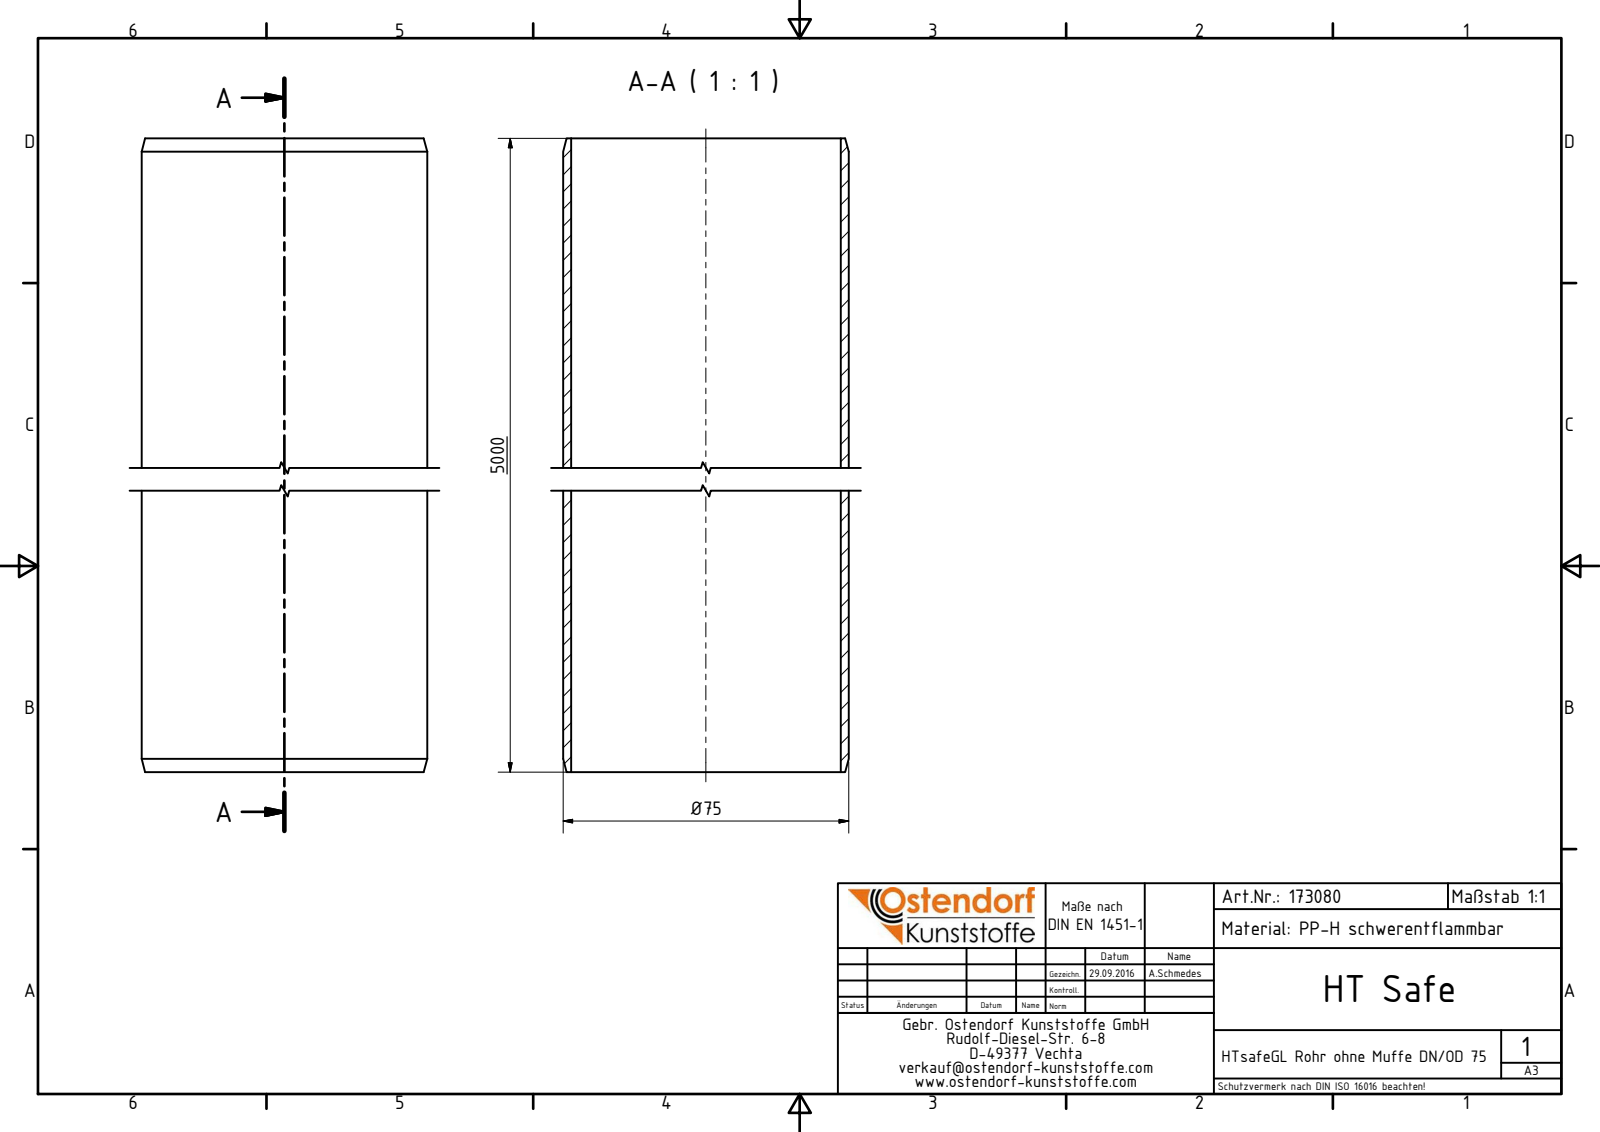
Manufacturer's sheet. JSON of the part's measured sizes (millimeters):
{"part_name": "173080 HTsafeGL DN_OD 75x5000", "step_written_by": "Autodesk Inventor 2016 (AUTOMOTIVE_DESIGN)", "units": "millimeters", "bodies": {"solids": 1, "faces": 6, "planar": 2, "cylindrical": 2, "other": 2}, "overall_size": [5000, 75, 75], "volume_mm3": 2404000, "surface_area_mm2": 2291000, "round_holes": [[70.8, 1]], "round_bosses_or_shafts": [[75, 1]], "face_to_face_distances": [5000]}
